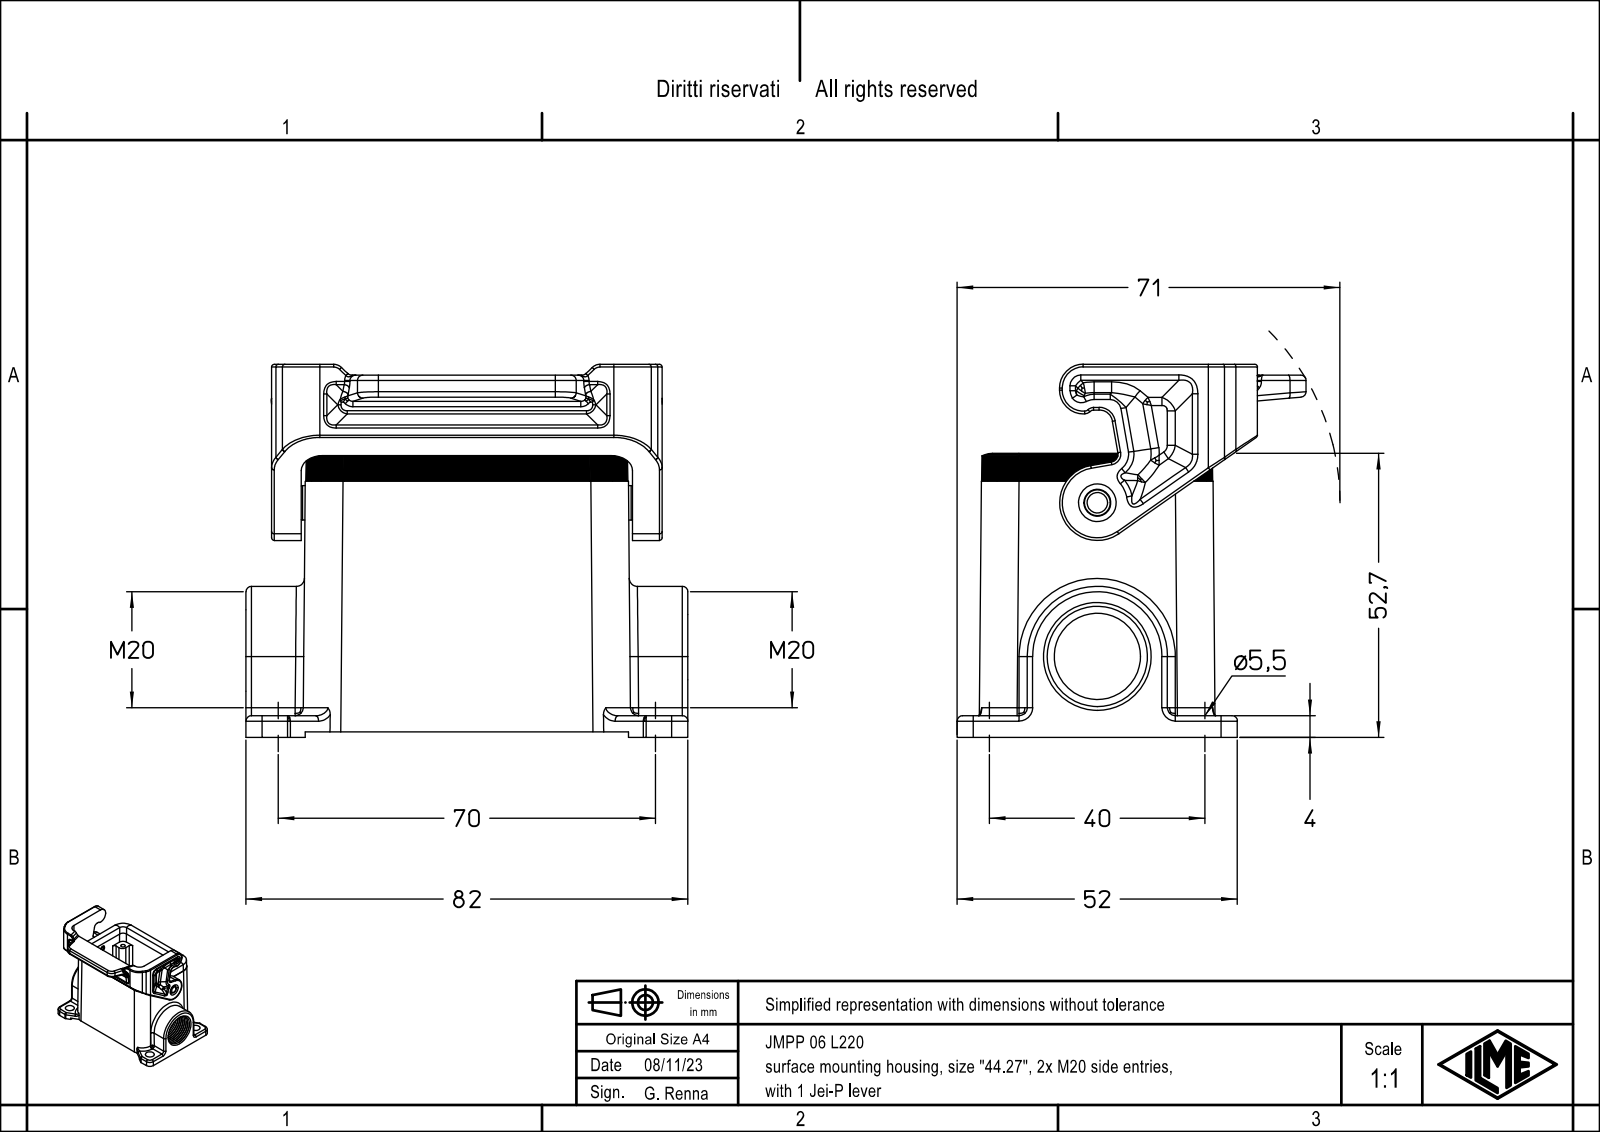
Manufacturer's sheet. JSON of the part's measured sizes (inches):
{"part_name": "JMPP 06 L220", "step_written_by": "Creo Elements/Direct Modeling 20.1B 02-Apr-2019 (C) Parametric Technology GmbH (AUTOMOTIVE_DESIGN)", "units": "inches", "bodies": {"solids": 1, "faces": 564, "planar": 118, "cylindrical": 196, "other": 250}, "overall_size": [3.228, 2.724, 2.549], "volume_in3": 4.726, "surface_area_in2": 54.6, "round_holes": [[0.217, 4], [0.63, 1], [0.732, 1]], "round_bosses_or_shafts": [[0.252, 1], [0.189, 1]], "partial_cylinders_radius": [[0.039, 35], [0.118, 28], [0.059, 24], [0.02, 20], [0.079, 16], [0.276, 9], [0.157, 8], [0.236, 6]], "face_to_face_distances": [0.118, 0.039, 0.157, 0.276, 0.404, 2.825, 2.421, 2.646, 2.606, 2.488], "hole_center_spacings": [1.575, 2.756, 3.174]}
